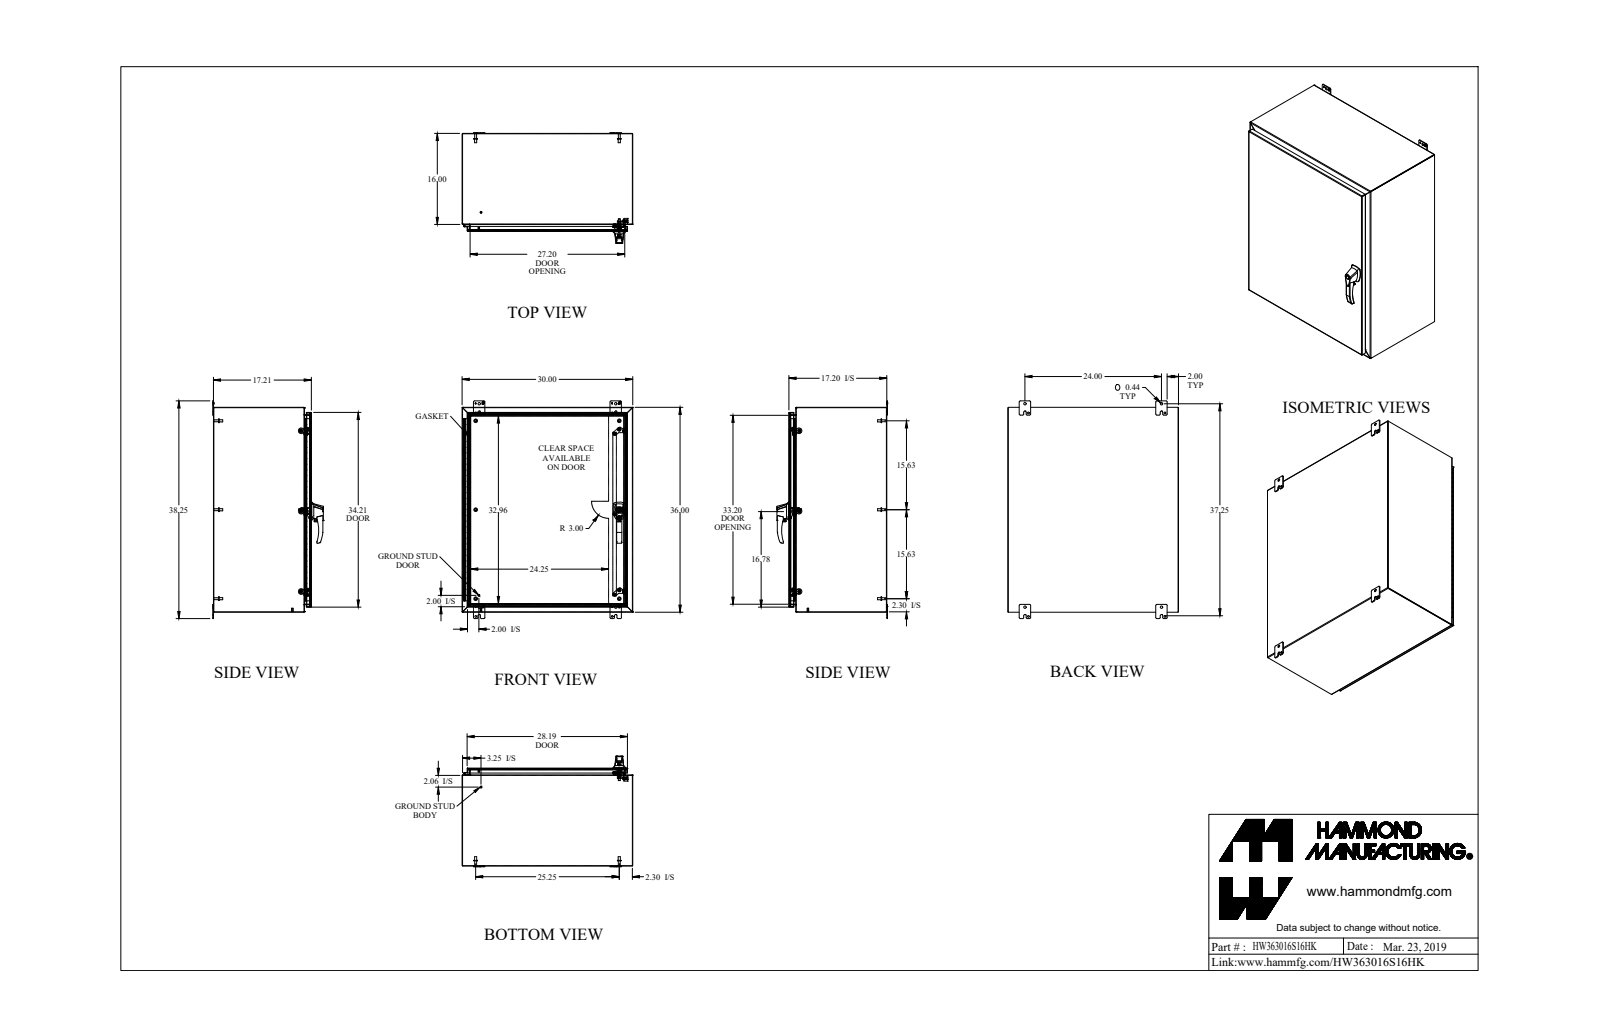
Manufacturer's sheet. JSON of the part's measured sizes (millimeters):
{"part_name": "HW363016S16HK", "step_written_by": "SolidWorks 2018 (AUTOMOTIVE_DESIGN)", "units": "millimeters", "bodies": {"solids": 46, "faces": 1506, "planar": 704, "cylindrical": 646, "other": 156}, "overall_size": [971.6, 762, 494], "volume_mm3": 6042000, "surface_area_mm2": 6339000, "round_holes": [[4.5, 6], [8, 5], [6.4, 3], [6.7, 3], [10.5, 3], [5, 2], [6.5, 2], [10, 2], [11.1, 2], [2.8, 1], [5.9, 1], [8.4, 1]], "round_bosses_or_shafts": [[9.5, 11], [6.4, 7], [16.5, 6], [8.4, 6], [4, 6], [25.4, 3], [13, 3], [16, 2]], "partial_cylinders_radius": [[6.4, 27], [4.8, 24], [0.9, 18], [2.7, 18], [1.5, 12], [3.2, 9], [1.1, 8], [5.5, 8]], "face_to_face_distances": [1.8, 760.2, 435.3, 433.5, 1.8, 435.3, 437.1, 912.6, 758.3, 762], "hole_center_spacings": [28.2, 358.6, 358.6, 717.2, 358.6, 609.6, 628, 949.5]}
